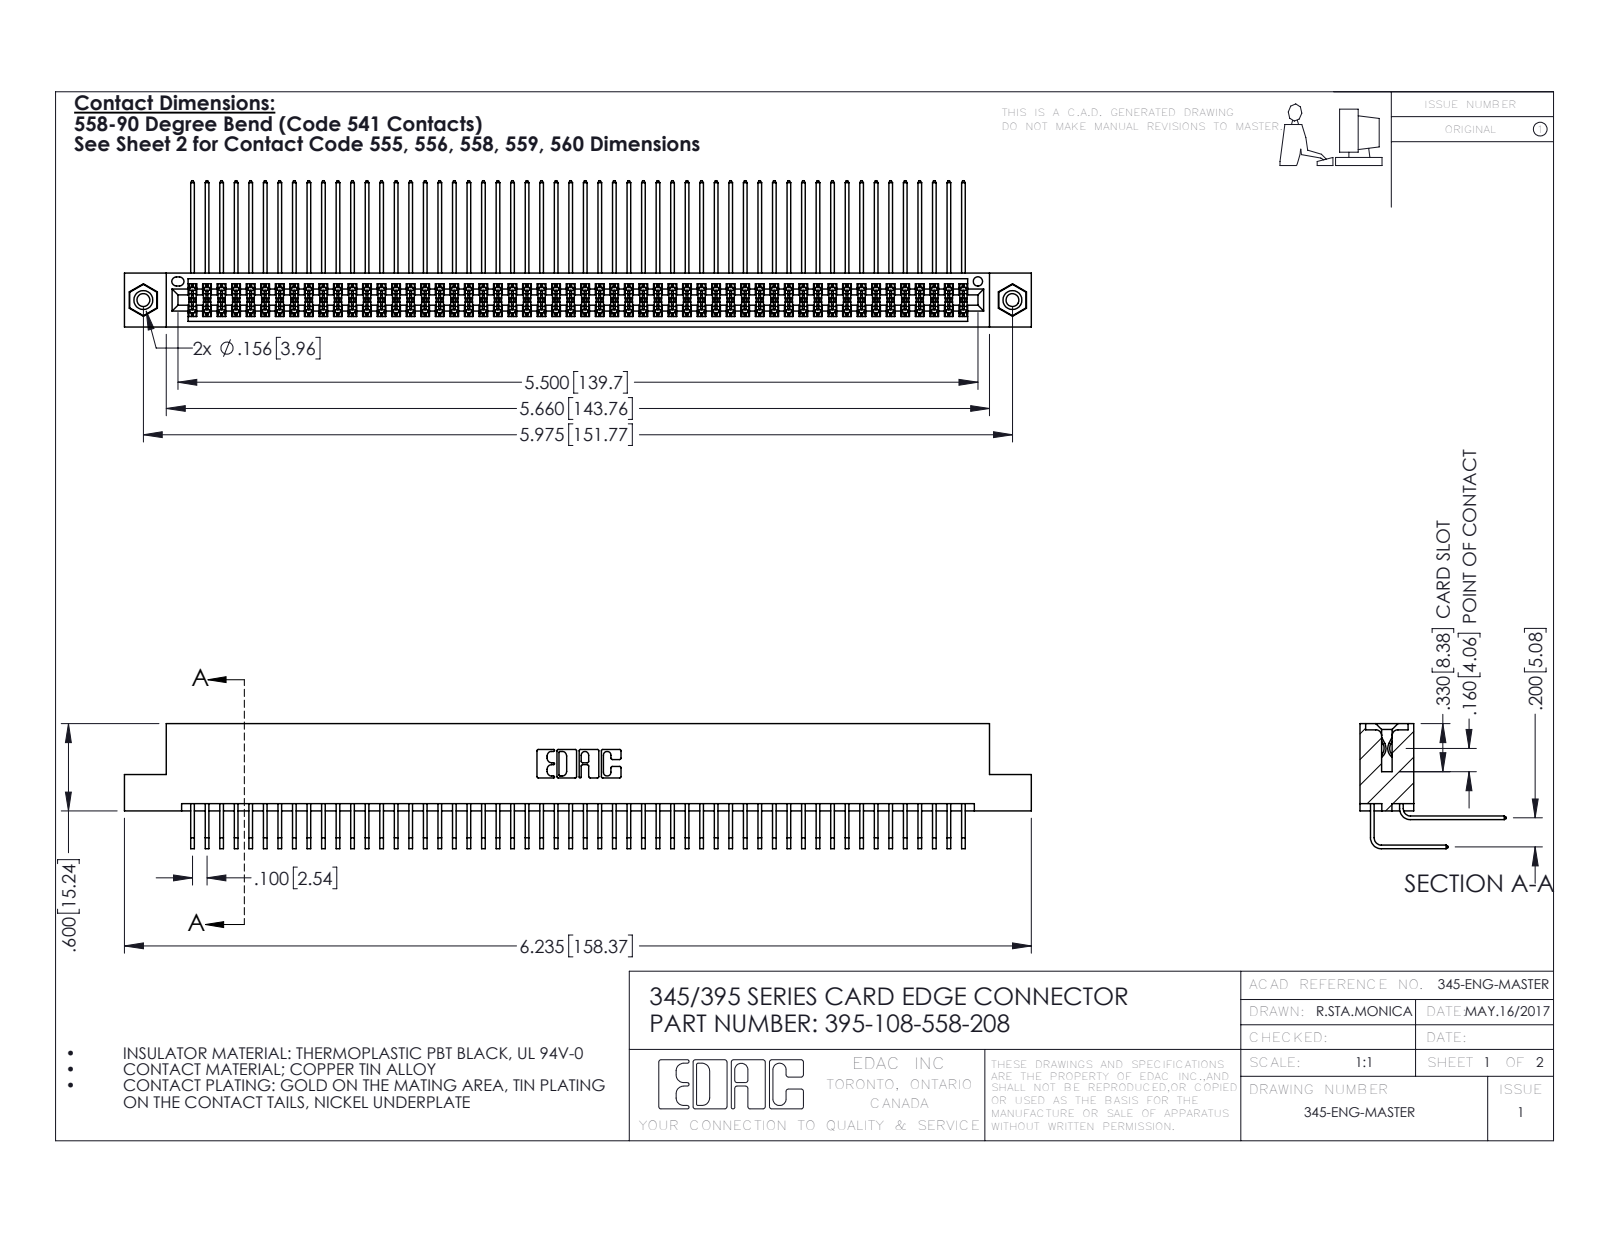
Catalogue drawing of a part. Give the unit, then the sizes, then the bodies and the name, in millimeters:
Units: millimetres
Overall size (bounding box): 158.4 × 25.5 × 21.8
Round holes (diameter × count): ⌀2.3 ×2, ⌀3.2 ×2, ⌀4 ×2, ⌀1.6 ×1
Round bosses / shafts (diameter × count): ⌀3.9 ×2
Partial cylindrical surfaces — rounded edges, fillets, slot ends (radius × count): R0.2 ×162, R0.3 ×22, R0.2 ×6, R0.8 ×6, R0.7 ×3, R0.4 ×2, R0.5 ×2, R0.6 ×2
Main face-to-face distances: 1.8, 7.6, 5.1, 9.4, 2.5, 6.9, 0.6, 5.7, 0.6, 4.4
Hole centre spacings: 6.9, 145.8, 151.8
Volume: 16 100 mm³ · Surface area: 26 990 mm²
Bodies: 111 solids, 5802 faces (3892 planar, 1894 cylindrical, 16 other)
Part name (STEP PRODUCT): 345-250-001_345-250-003-102; 345-292-001_558 Tail - 2; 345 Part_Flush Mounting Lugs - 0.156 Dia-TI; 345-292-001_558 559 Tail - 1 (+1 more)
STEP written by: SolidWorks 2016 (CONFIG_CONTROL_DESIGN)
